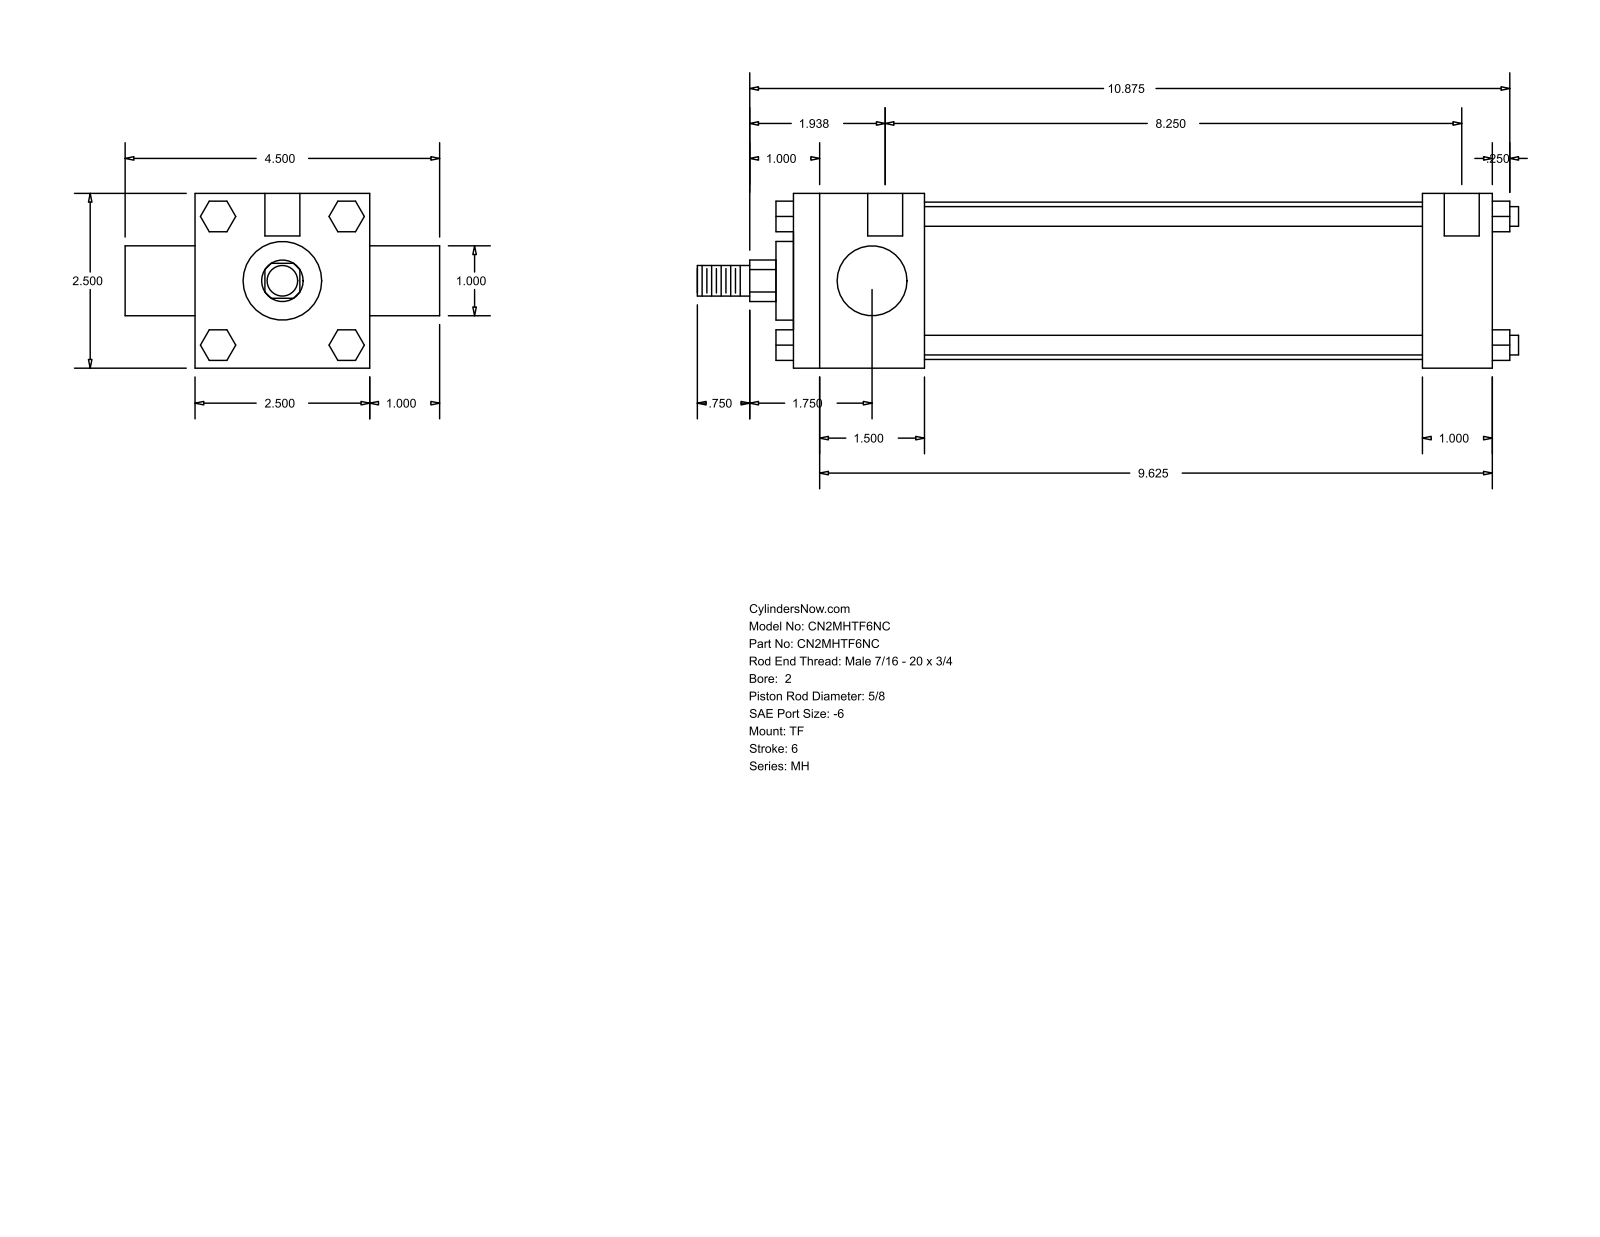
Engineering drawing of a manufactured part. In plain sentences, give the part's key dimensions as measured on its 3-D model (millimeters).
The part is named "MH_TF__0200_0.625". Its 3-D file was written by "GSSL Pune (CONFIG_CONTROL_DESIGN)". It is 0 solids with 120 faces: 92 planar, 28 cylindrical and 0 other. Overall it measures 298.45 by 114.3 by 63.5 millimeters. Round holes: 3 of diameter 5.56, 2 of diameter 12.7. Round bosses or shafts: 4 of diameter 7.14, 1 of diameter 57.15, 1 of diameter 28.57, 1 of diameter 25.4, 1 of diameter 15.88, 1 of diameter 11.11. Partial cylindrical surfaces (rounded edges, fillets, slot ends): 1 of radius 7.54. The main face-to-face distances are 63.5, 254, 47.62, 228.59, 180.97, 206.38, 25.41, 25.4, 6.35, 88.9. The hole center spacings are 3.18, 4.76, 209.55, 212.73, 214.31, 217.49.
